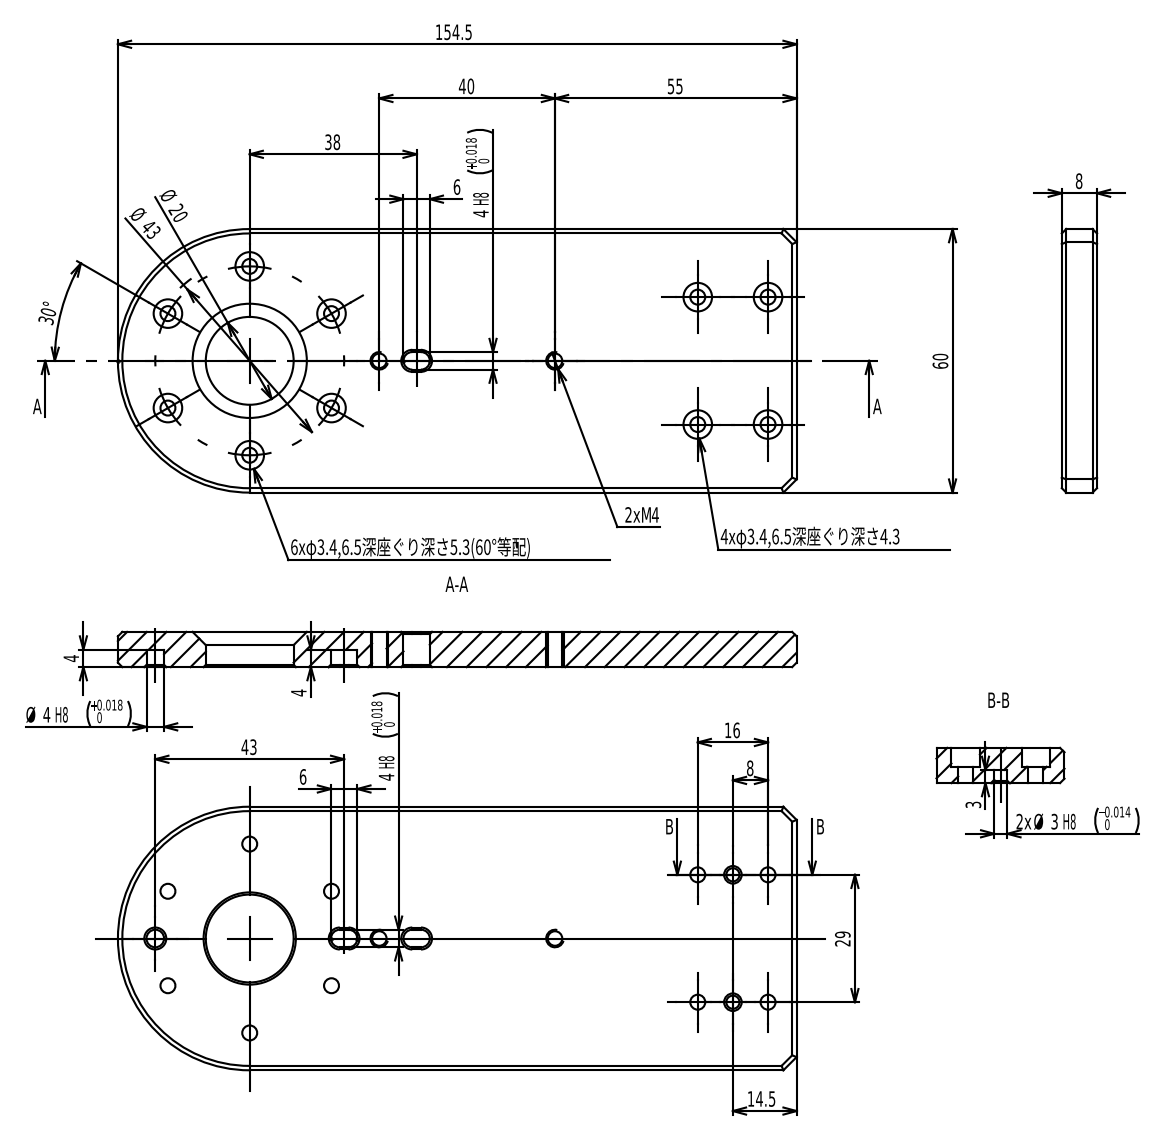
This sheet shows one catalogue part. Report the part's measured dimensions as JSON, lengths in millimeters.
{"part_name": "PDG60-1", "step_written_by": "SolidWorks 2020 (CONFIG_CONTROL_DESIGN)", "units": "millimeters", "bodies": {"solids": 1, "faces": 122, "planar": 41, "cylindrical": 59, "other": 22}, "overall_size": [154.5, 60, 8], "volume_mm3": 65373, "surface_area_mm2": 21758, "round_holes": [[3.4, 10], [6.5, 10], [3, 2], [3.3, 2], [4, 1], [20, 1]], "partial_cylinders_radius": [[2, 4], [30, 1]], "face_to_face_distances": [8, 60, 46.66, 5.3, 2.7, 1, 4.3, 3.7, 4, 28], "hole_center_spacings": [21.5, 37.24, 8, 30.08, 29, 43, 11.13, 15.29]}
